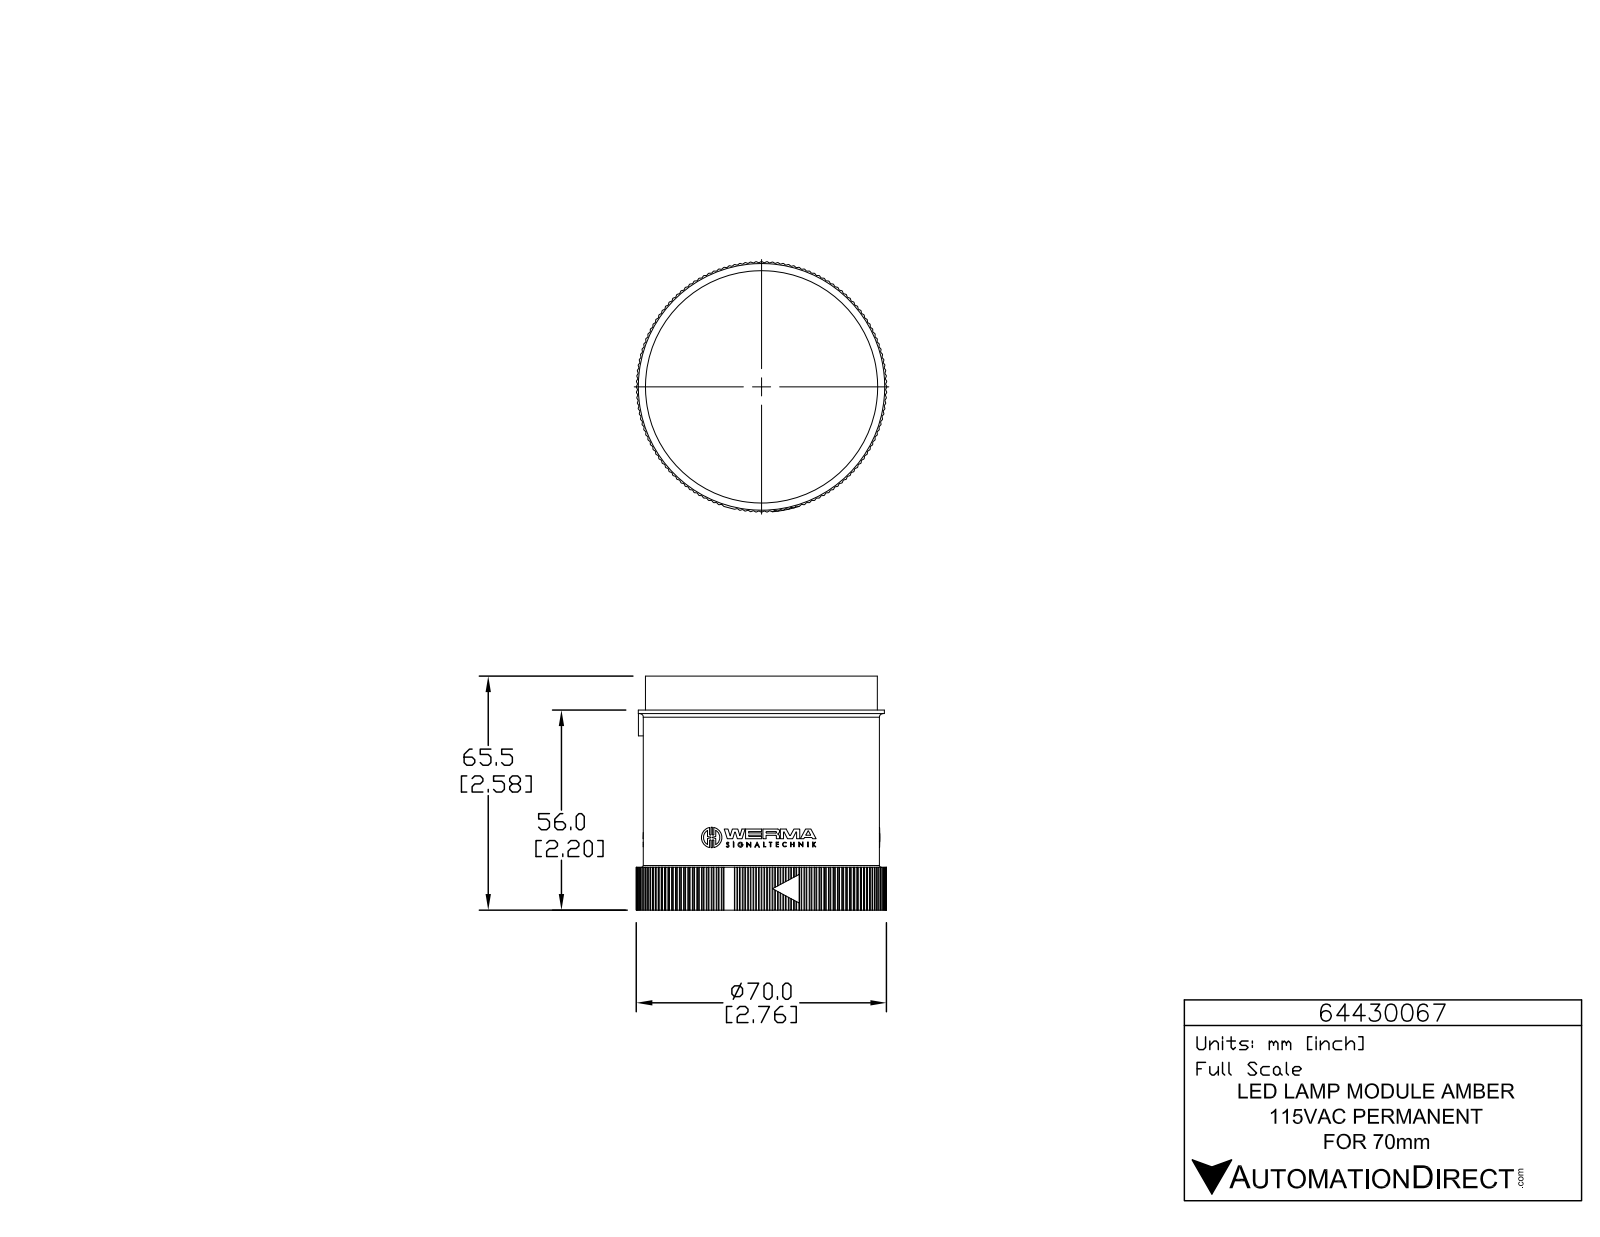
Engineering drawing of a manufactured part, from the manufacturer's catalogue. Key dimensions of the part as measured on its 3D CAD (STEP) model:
Part name (STEP PRODUCT): 64430067
STEP written by: SolidWorks 2015 (AUTOMOTIVE_DESIGN)
Units: inches
Bodies: 1 solid, 1400 faces (832 planar, 563 cylindrical, 5 other)
Overall size (bounding box): 2.762 × 2.762 × 2.579
Volume: 12.02 in³ · Surface area: 37.48 in²
Round holes (diameter × count): ⌀0.039 ×3, ⌀2.575 ×1
Round bosses / shafts (diameter × count): ⌀0.226 ×3, ⌀0.056 ×3, ⌀2.717 ×1, ⌀2.606 ×1, ⌀2.559 ×1
Partial cylindrical surfaces — rounded edges, fillets, slot ends (radius × count): R0.008 ×285, R0.008 ×6, R0.008 ×6, R0.008 ×6, R0.131 ×6, R0.004 ×3, R0.005 ×3, R0.008 ×3
Main face-to-face distances: 2.201, 2.451, 0.378, 2.579, 2.205, 1.827, 0.374, 2.452, 0.472, 0.094
